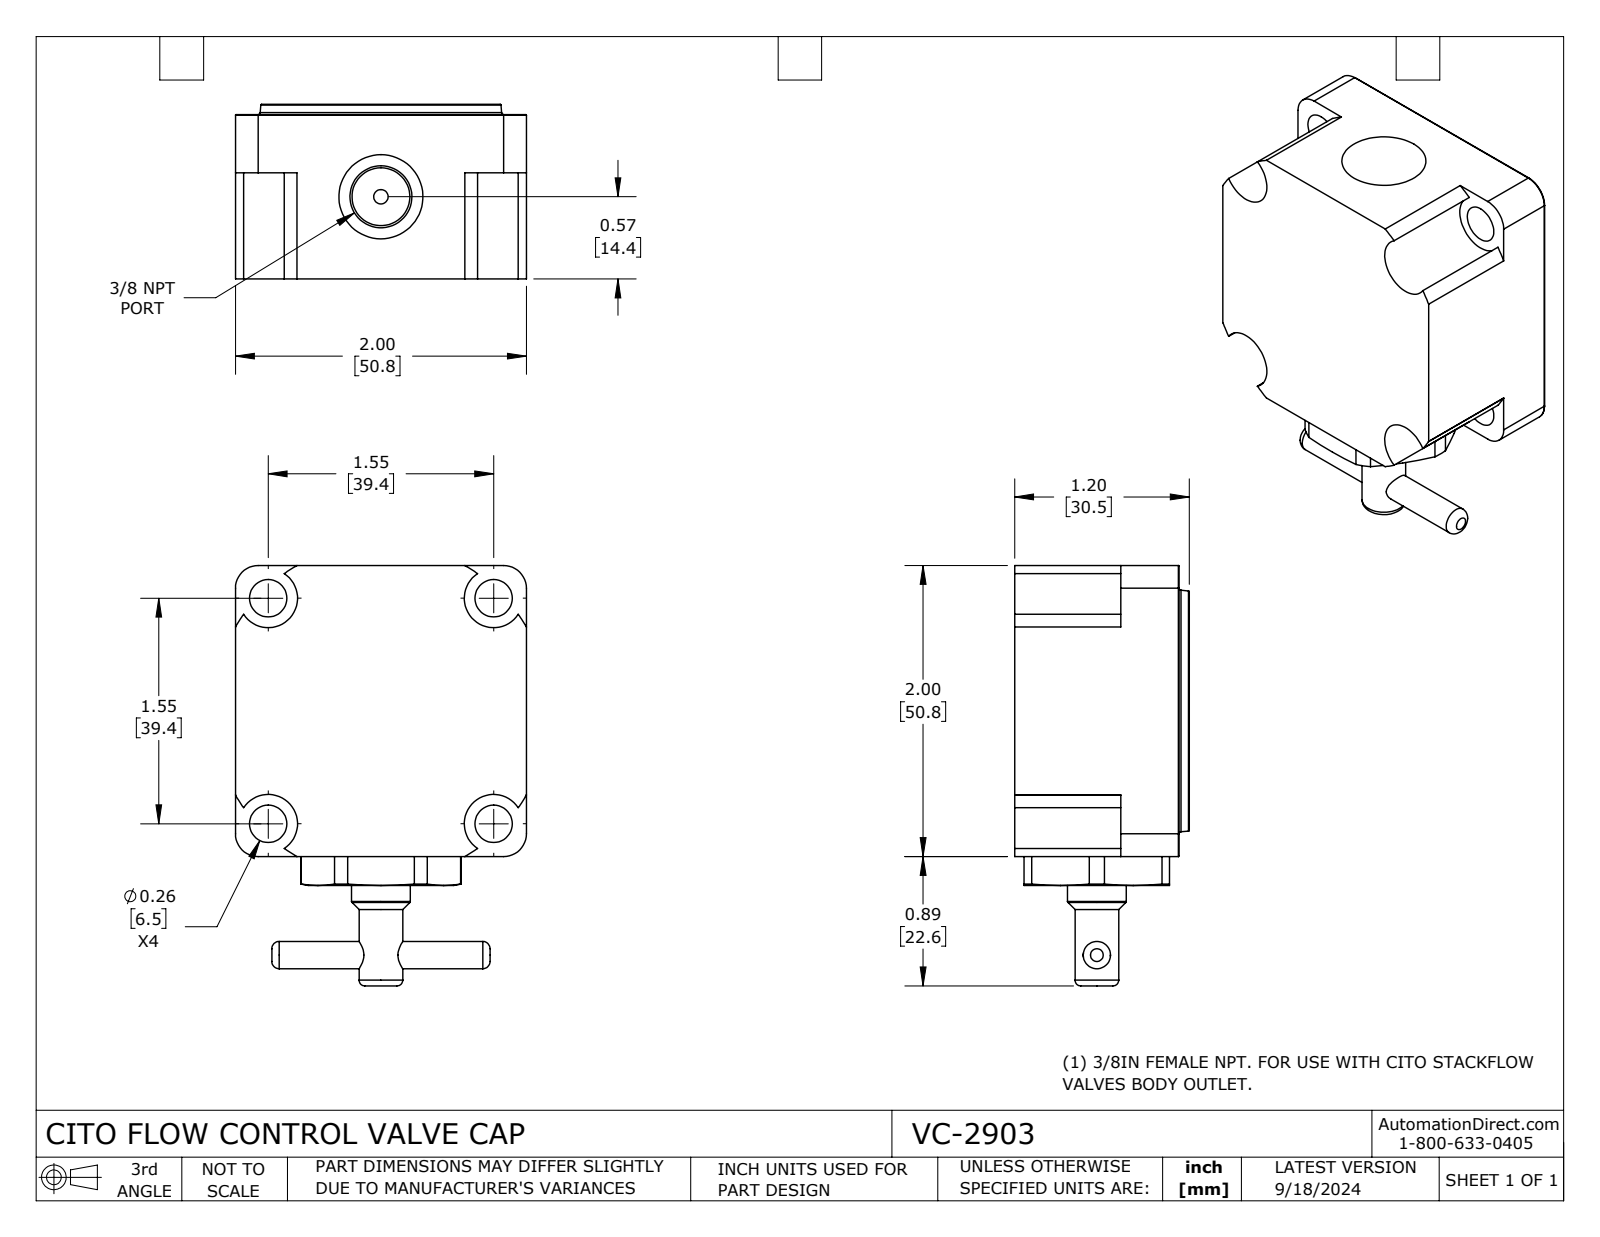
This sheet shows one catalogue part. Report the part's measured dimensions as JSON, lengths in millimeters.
{"part_name": "VC-2903", "step_written_by": "SolidWorks 2023 (CONFIG_CONTROL_DESIGN)", "units": "millimeters", "bodies": {"solids": 4, "faces": 284, "planar": 40, "cylindrical": 130, "other": 114}, "overall_size": [73.4, 50.8, 30.5], "volume_mm3": 57140, "surface_area_mm2": 20660, "round_holes": [[6.5, 4], [4.8, 1], [10.2, 1], [10.8, 1], [11.7, 1], [14.7, 1], [16.2, 1], [23.1, 1]], "round_bosses_or_shafts": [[25.5, 1], [24.8, 1], [23.1, 1], [12.6, 1], [12.5, 1], [11.7, 1], [10.2, 1], [7.6, 1]], "partial_cylinders_radius": [[0.1, 5], [4, 4], [5.1, 4], [6.4, 4], [6.7, 1], [13.2, 1], [14, 1], [29.3, 1]], "face_to_face_distances": [50.8, 28.7, 1.8, 30.5, 25.4, 3.3, 10.2, 27.2, 5.1, 55.9], "hole_center_spacings": [39.4, 39.4, 55.7, 55.7]}
